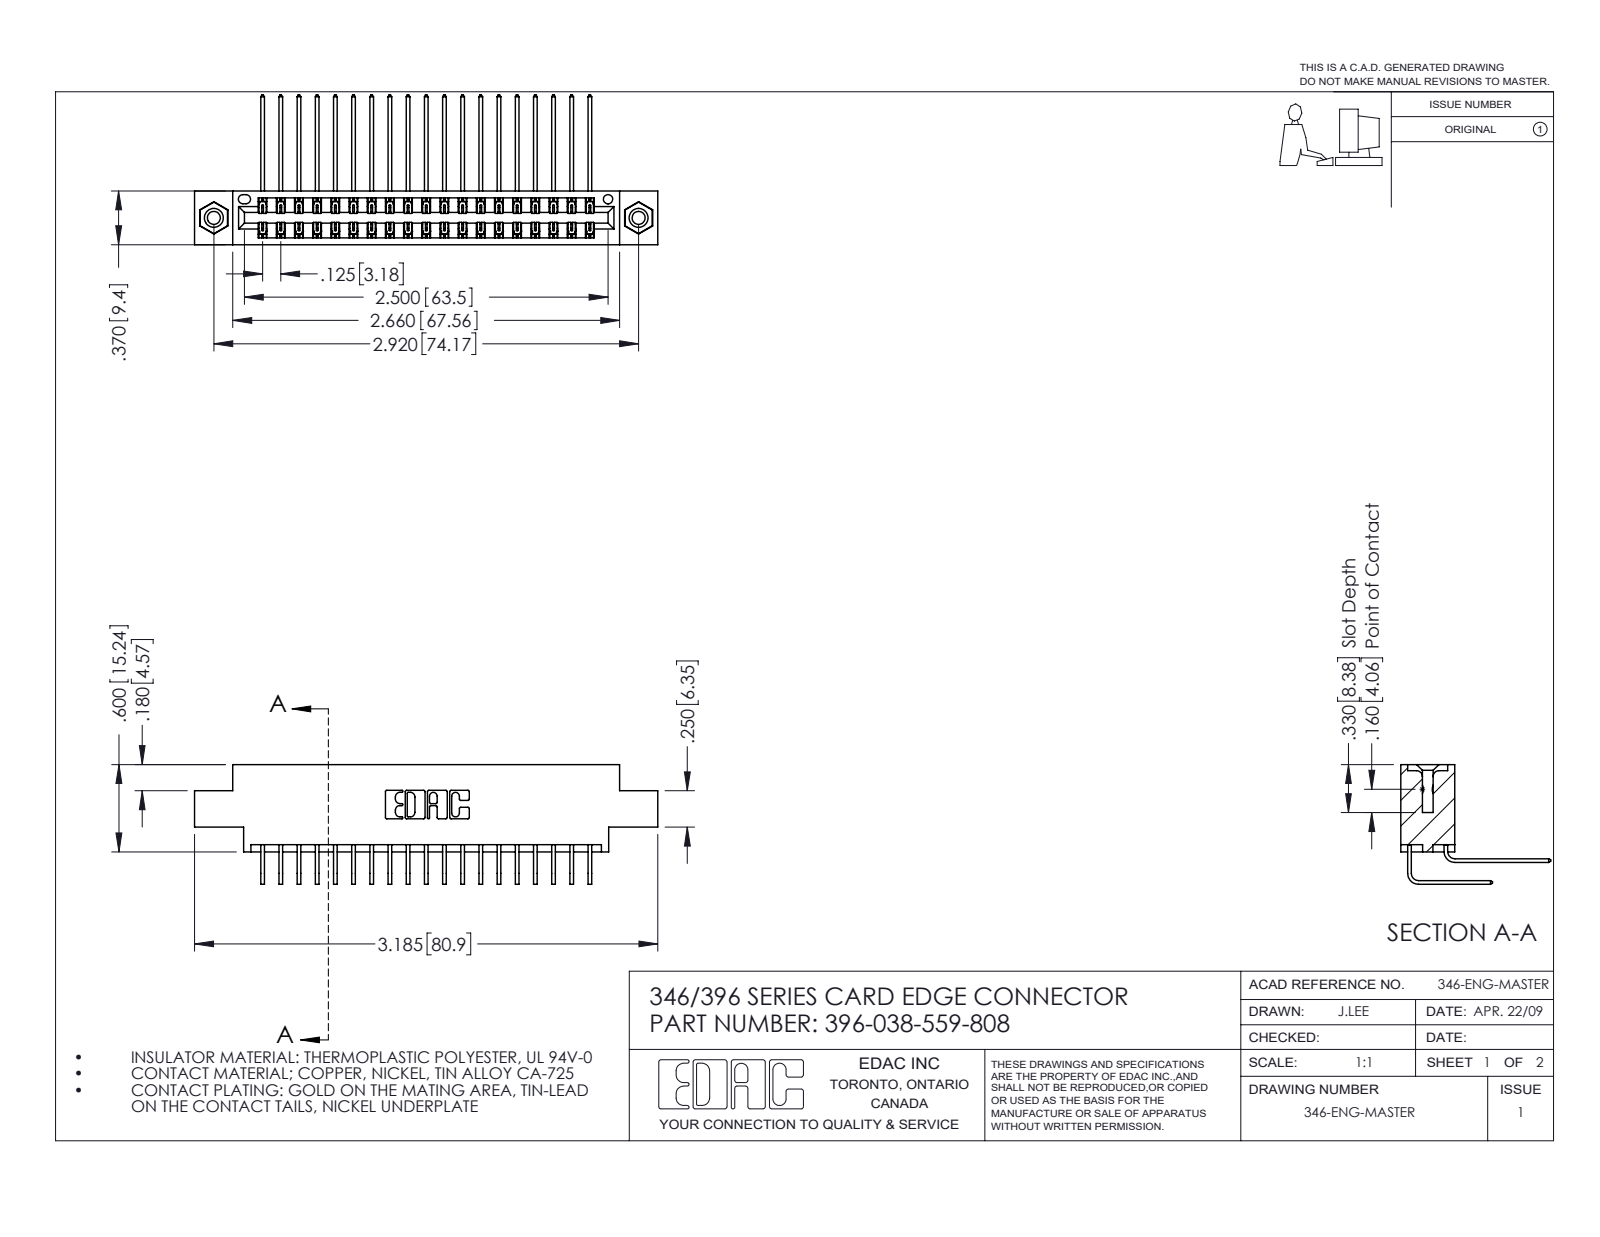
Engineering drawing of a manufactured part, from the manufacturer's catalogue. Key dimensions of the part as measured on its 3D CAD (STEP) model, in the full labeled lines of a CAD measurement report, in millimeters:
Part name (STEP PRODUCT): 345-292-001_559 Tail - 2; 396-038-559-808; 346 Part_0.170 Offset - 0.156 Dia-TI; 345-250-001_345-250-003-102 (+1 more)
STEP written by: SolidWorks 2016 (CONFIG_CONTROL_DESIGN)
Units: millimetres
Bodies: 41 solids, 2238 faces (1518 planar, 704 cylindrical, 16 other)
Overall size (bounding box): 80.9 × 26.2 × 20.9
Volume: 7 770 mm³ · Surface area: 11 570 mm²
Round holes (diameter × count): ⌀2.3 ×2, ⌀3.2 ×2, ⌀4 ×2, ⌀1.6 ×1
Round bosses / shafts (diameter × count): ⌀3.9 ×2
Partial cylindrical surfaces — rounded edges, fillets, slot ends (radius × count): R0.2 ×57, R0.3 ×22, R0.2 ×6, R0.8 ×6, R0.7 ×3, R0.4 ×2, R0.6 ×2, R0.6 ×2
Main face-to-face distances: 1.2, 8.2, 9.4, 0.6, 6.4, 1.8, 7.6, 7, 5.6, 3.8
Hole centre spacings: 6.2, 68.9, 74.2
